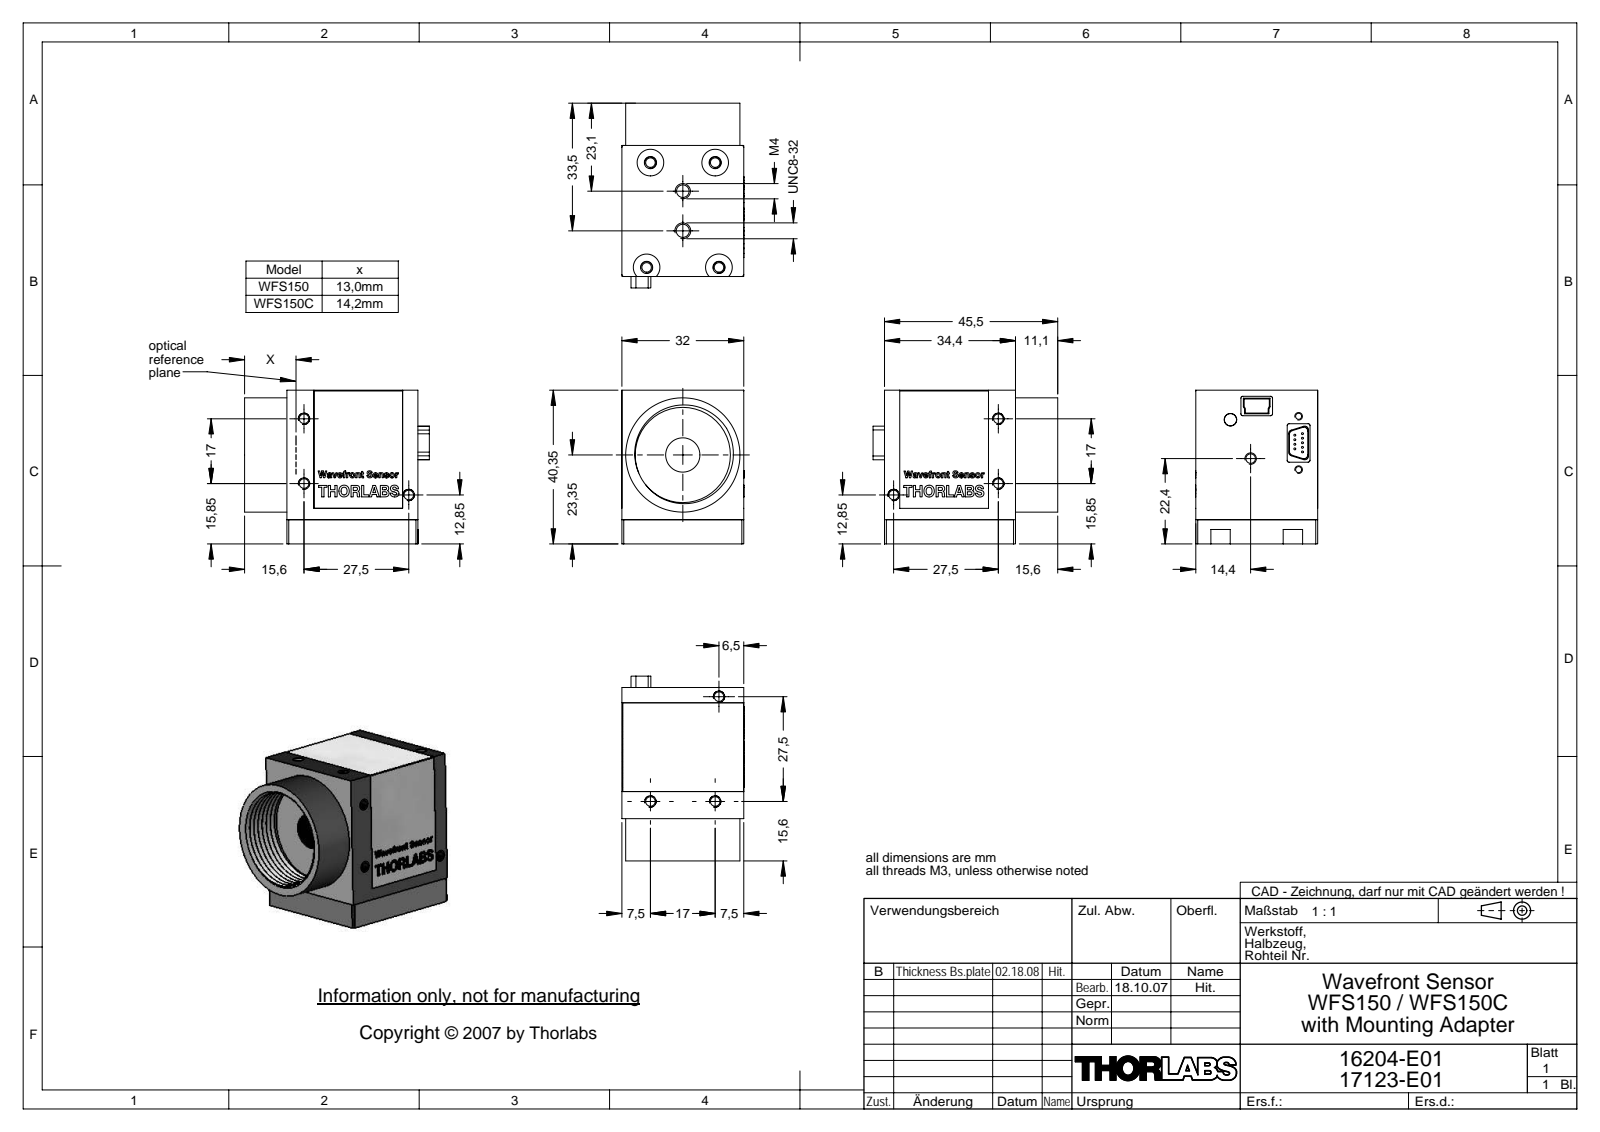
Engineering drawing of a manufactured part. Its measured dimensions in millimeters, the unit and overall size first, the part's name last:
Units: millimetres
Overall size (bounding box): 48.5 × 40.35 × 32.05
Round holes (diameter × count): ⌀1.6 ×8, ⌀2.5 ×8, ⌀3.2 ×4, ⌀3.3 ×2, ⌀7 ×2, ⌀3.45 ×1, ⌀9 ×1, ⌀25 ×1
Round bosses / shafts (diameter × count): ⌀0.5 ×9, ⌀30 ×1, ⌀3.2 ×1
Partial cylindrical surfaces — rounded edges, fillets, slot ends (radius × count): R0.5 ×12, R1 ×8, R3.5 ×2
Main face-to-face distances: 34, 34.4, 6.35, 40.35, 31.8, 32, 45.5, 11.1, 3.8, 2.55
Hole centre spacings: 12, 3.2, 3.54, 6.36, 7, 8.28, 10.9, 11.24
Volume: 44 804 mm³ · Surface area: 14 106 mm²
Bodies: 3 solids, 908 faces (461 planar, 123 cylindrical, 324 other)
Part name (STEP PRODUCT): 16204_17123 Wavefrontsensor mit Basisplatte
STEP written by: SolidWorks 2008 (CONFIG_CONTROL_DESIGN)
